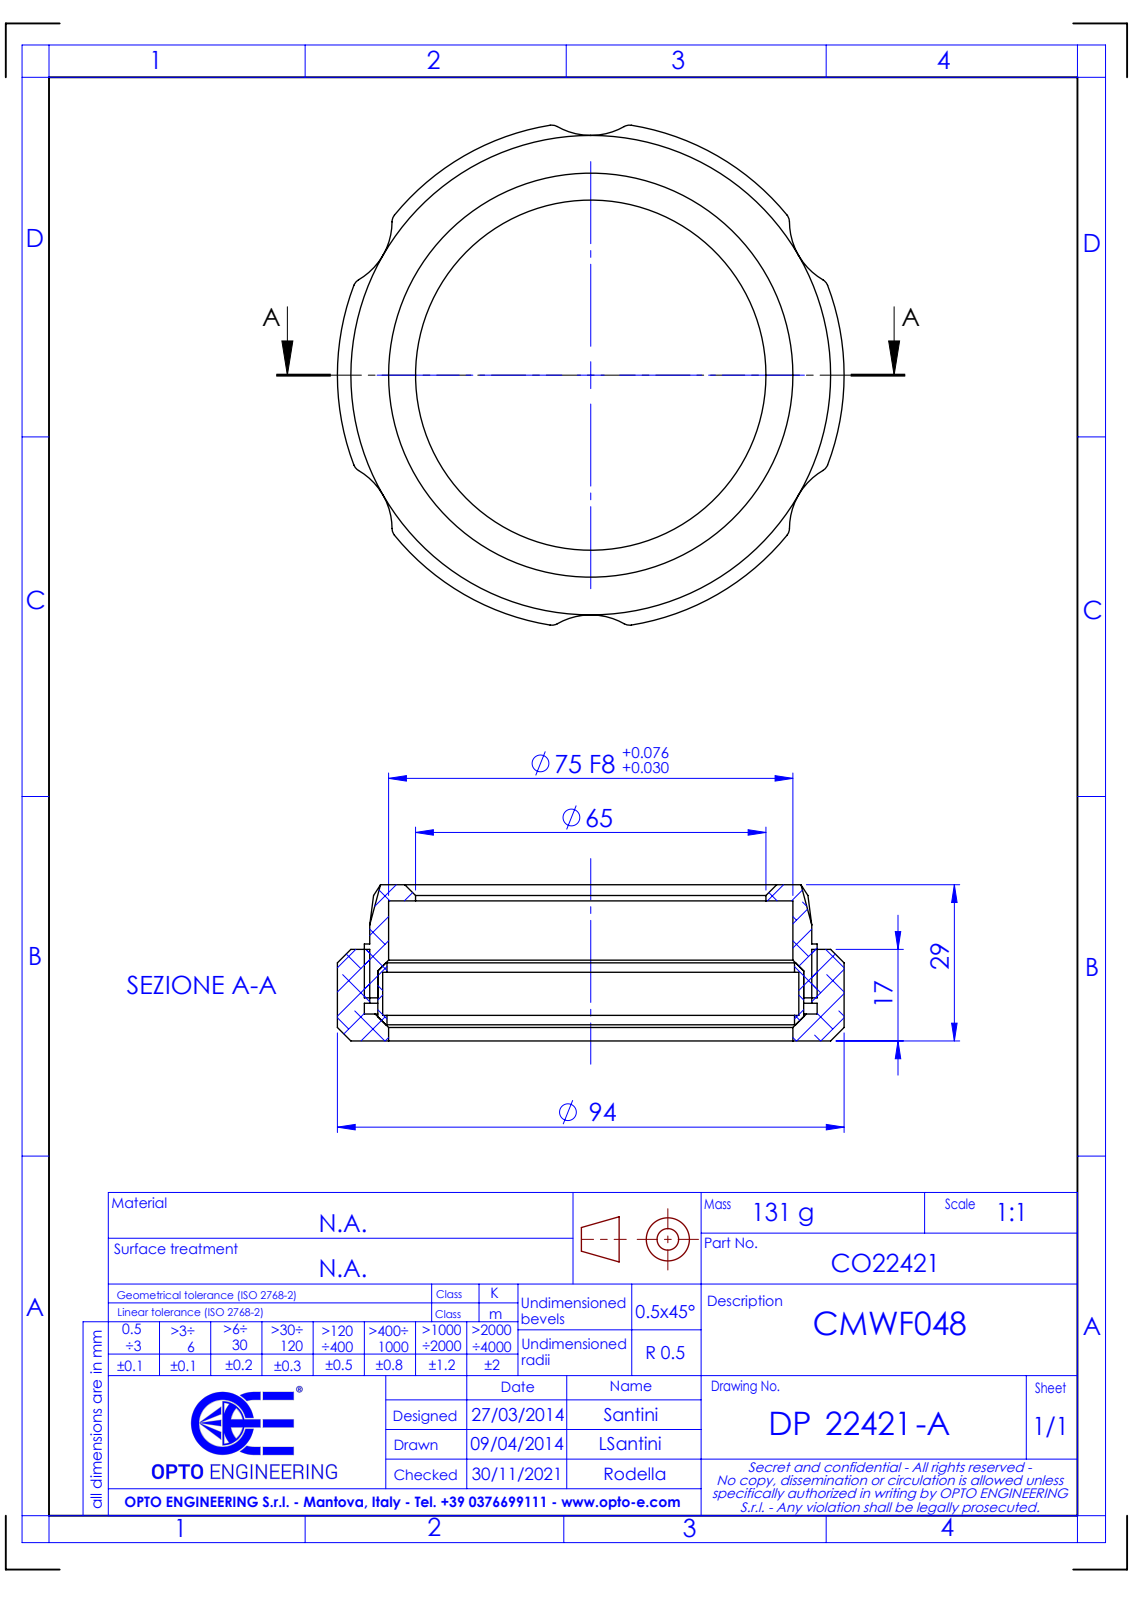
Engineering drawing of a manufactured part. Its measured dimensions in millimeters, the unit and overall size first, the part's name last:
Units: millimetres
Overall size (bounding box): 94 × 92.84 × 29
Round holes (diameter × count): ⌀65 ×1, ⌀75 ×1, ⌀75.6 ×1, ⌀77.2 ×1, ⌀79 ×1, ⌀82 ×1, ⌀84 ×1
Partial cylindrical surfaces — rounded edges, fillets, slot ends (radius × count): R2 ×12, R12.5 ×6, R40 ×6, R47 ×1
Main face-to-face distances: 3, 9, 12, 21, 26, 8, 29, 17, 18, 5
Bodies: 0 solids, 102 faces (14 planar, 62 cylindrical, 26 other)
Part name (STEP PRODUCT): DP22421 -A_CMWF048
STEP written by: SolidWorks 2021 (CONFIG_CONTROL_DESIGN)
